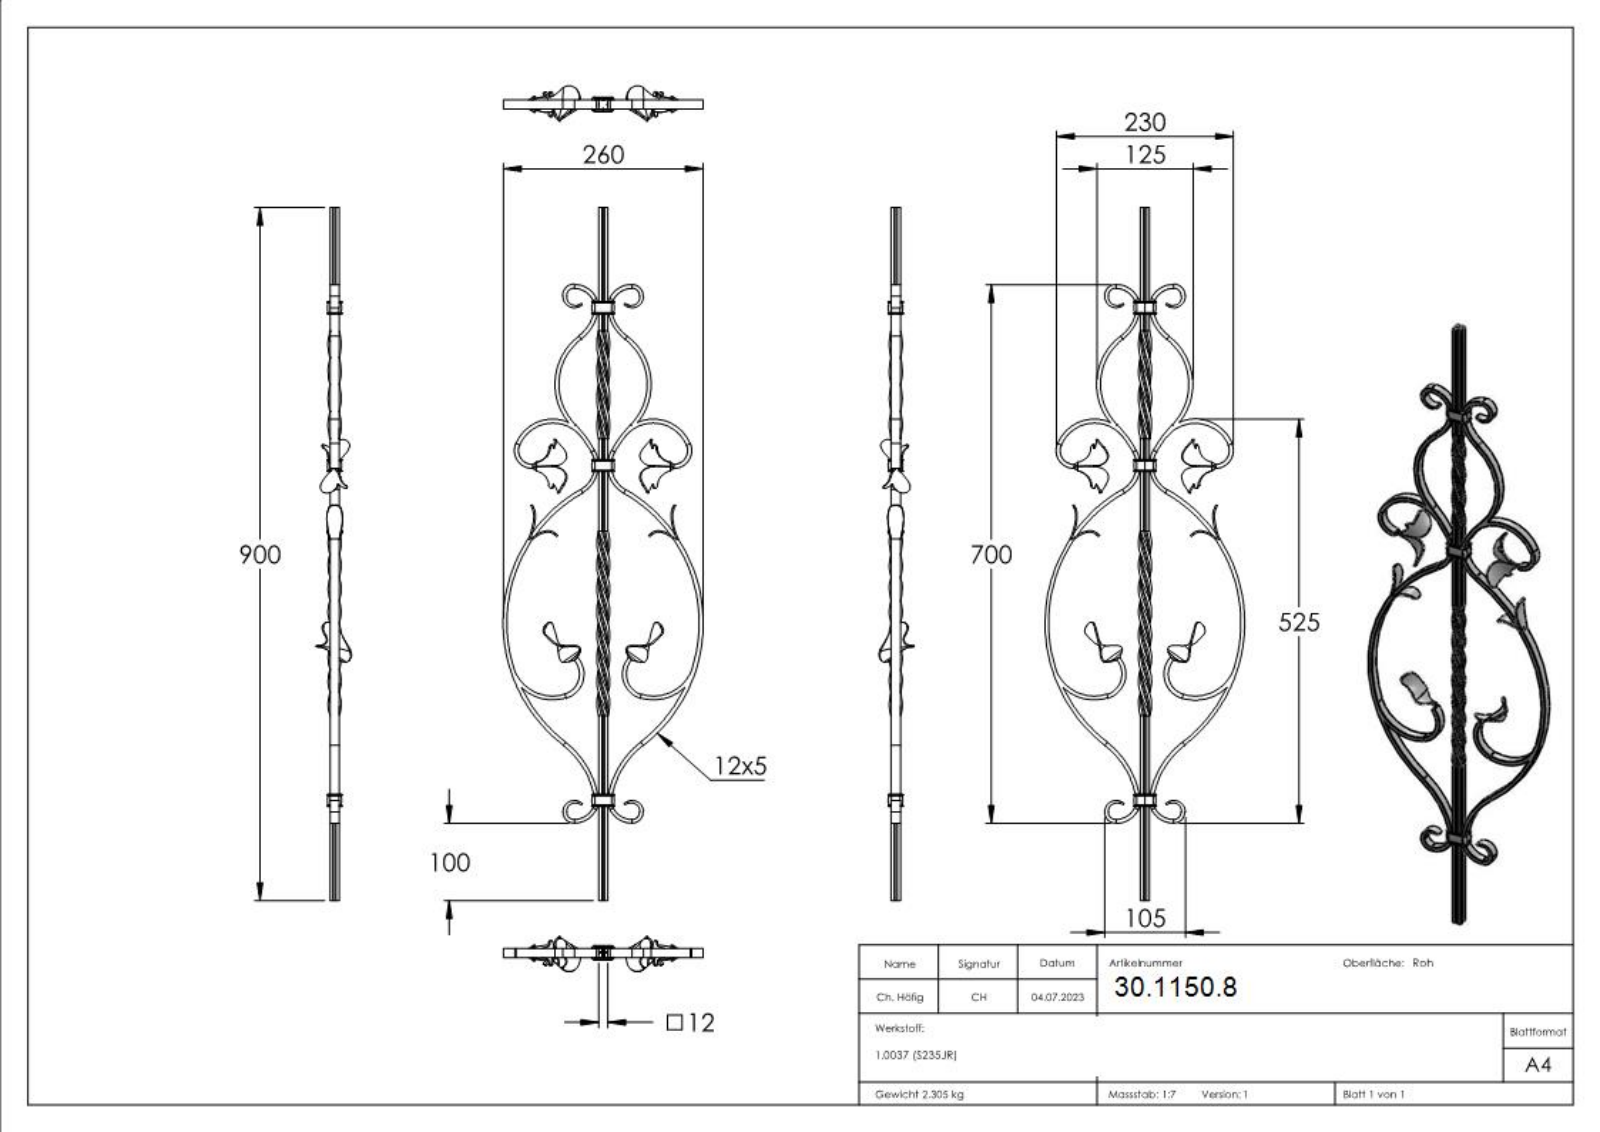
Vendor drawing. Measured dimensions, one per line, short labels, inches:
name: 1503
written by: SolidWorks 2018 (CONFIG_CONTROL_DESIGN)
unit: in
bodies: 5 solids, 1017 faces (387 planar, 251 cylindrical, 379 other)
size: 35.433 × 10.236 × 1.812
volume: 18.04 in³; area: 246.5 in²
rounds: 64× R0.02, 24× R0.008, 12× R0.851, 8× R0.197, 4× R0.039, 4× R0.157, 4× R0.394, 4× R0.591
face distances: 0.472, 0.352, 0.492, 0.02, 0.512, 0.217, 0.689, 0.63, 17.126, 0.906
